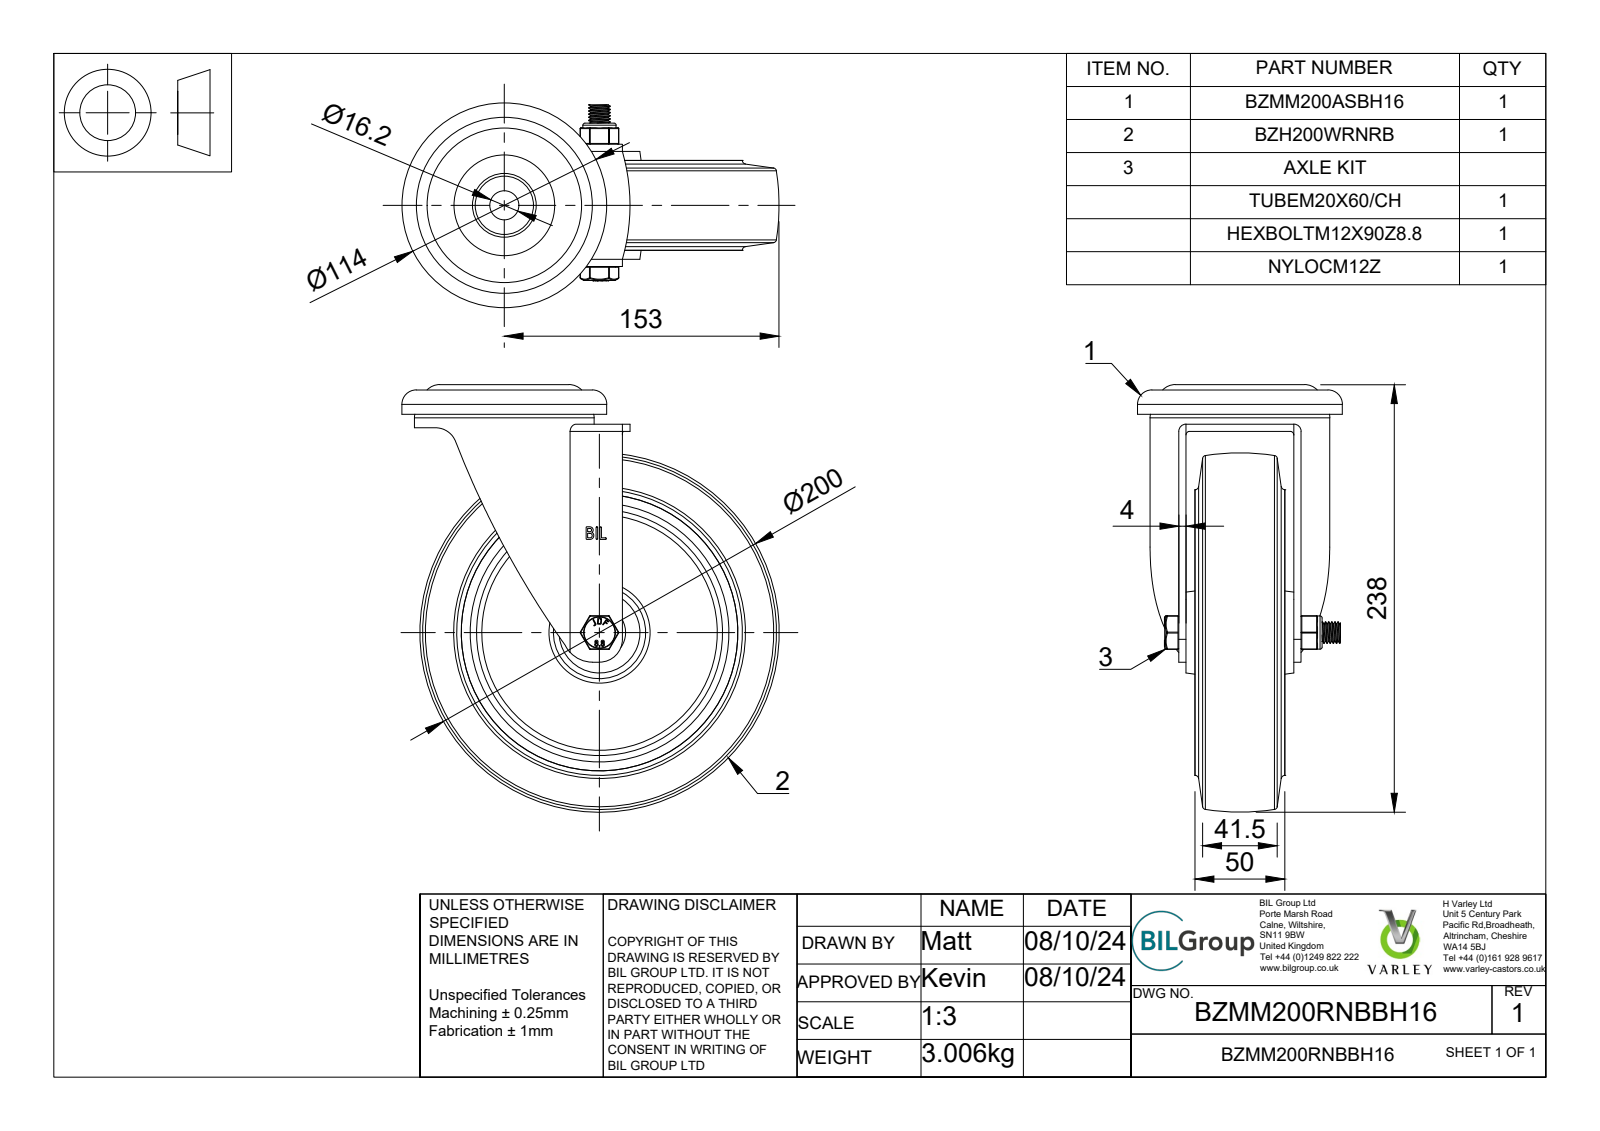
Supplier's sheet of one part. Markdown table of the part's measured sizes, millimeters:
| quantity | value |
| --- | --- |
| part name | BZMM200RNBBH16 v3; BZMM200ASBH16 v1; ZINC PLATED, PRESSED STEEL HEAD; ZINC PLATED, PRESSED STEEL FORKS (+7 more) |
| STEP written by | Autodesk Translation Framework v13.20.0.188 (AUTOMOTIVE_DESIGN) |
| units | millimeters |
| bodies | 19 solids, 467 faces (217 planar, 151 cylindrical, 99 other) |
| overall size | 238 × 210 × 114 |
| volume | 1 154 000 mm³ |
| surface area | 292 650 mm² |
| round holes (diameter × count) | 4.7 × 10, 12 × 1, 12.2 × 1, 12.5 × 1, 14 × 1, 16.2 × 1, 20 × 1, 29 × 1, 41 × 1, 52 × 1, 92 × 1, 104 × 1 |
| round bosses / shafts (diameter × count) | 4.5 × 10, 159 × 1, 114 × 1, 100 × 1, 74 × 1, 47 × 1, 32.5 × 1, 19.9 × 1 |
| partial cylindrical surfaces (radius × count) | 0.5 × 19, 0.47 × 4, 0.9 × 4, 2 × 4, 0.89 × 2, 0.89 × 2, 4 × 2, 6.78 × 2 |
| main face-to-face distances | 9, 29.5, 5, 25.5, 34.5, 4, 55, 64, 38.5, 59 |
| hole center spacings | 12.25, 14.4, 19.82, 23.3, 7.57, 24.5, 7.58 |
